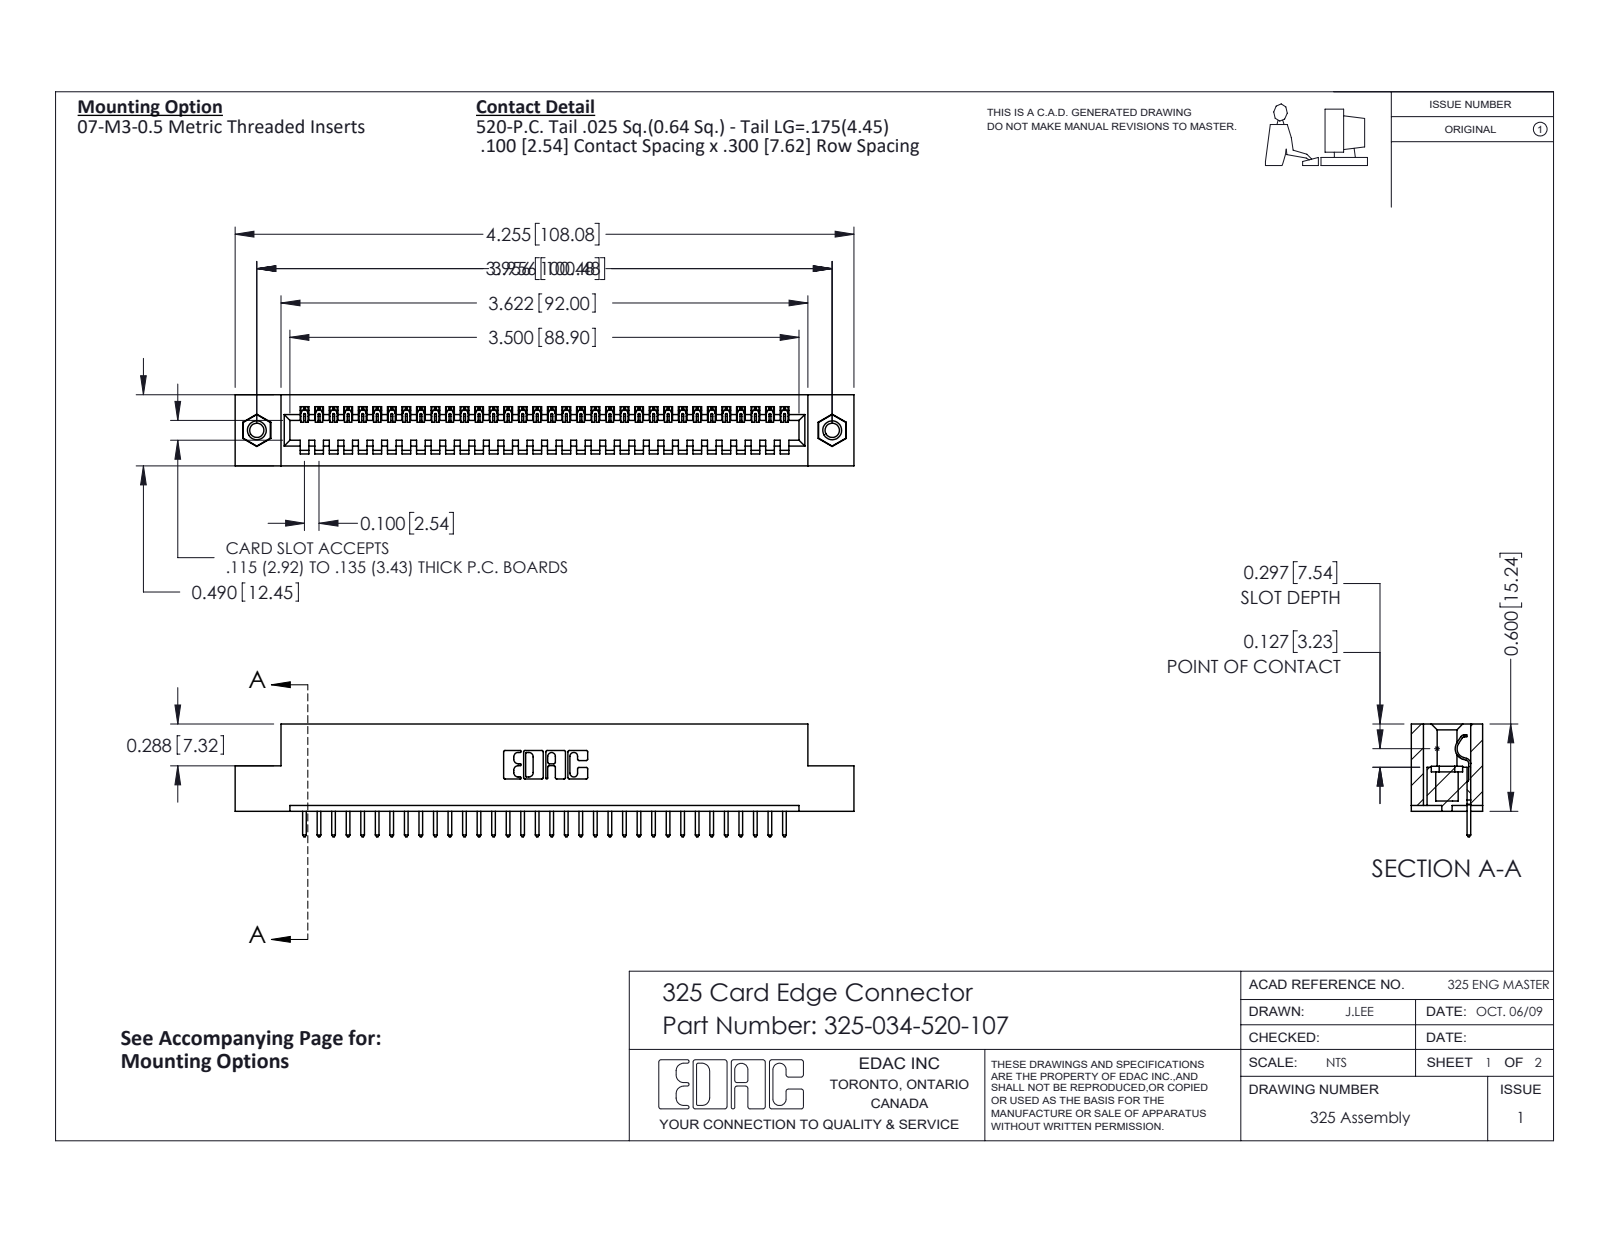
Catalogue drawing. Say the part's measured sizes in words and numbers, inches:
The part is named "345-250-001_345-250-005-103; 325-034-520-107; 325-292-001_325-293-120; 325 Part_TI". Its 3-D file was written by "SolidWorks 2016 (CONFIG_CONTROL_DESIGN)". It is 37 solids with 2146 faces: 1530 planar, 600 cylindrical and 16 other. Overall it measures 4.255 by 0.775 by 0.49 inches. Its volume is 0.827 cubic inches and its surface area 22.23 square inches. Round holes: 2 of diameter 0.098, 2 of diameter 0.125, 2 of diameter 0.16. Round bosses or shafts: 2 of diameter 0.155. Partial cylindrical surfaces (rounded edges, fillets, slot ends): 68 of radius 0.006, 68 of radius 0.01, 22 of radius 0.01, 6 of radius 0.007, 6 of radius 0.031, 3 of radius 0.026, 1 of radius 0.014, 1 of radius 0.022. The main face-to-face distances are 0.083, 0.407, 0.49, 0.3, 0.107, 0.383, 0.025, 0.325, 0.04, 0.56. The hole center spacings are 3.956.
